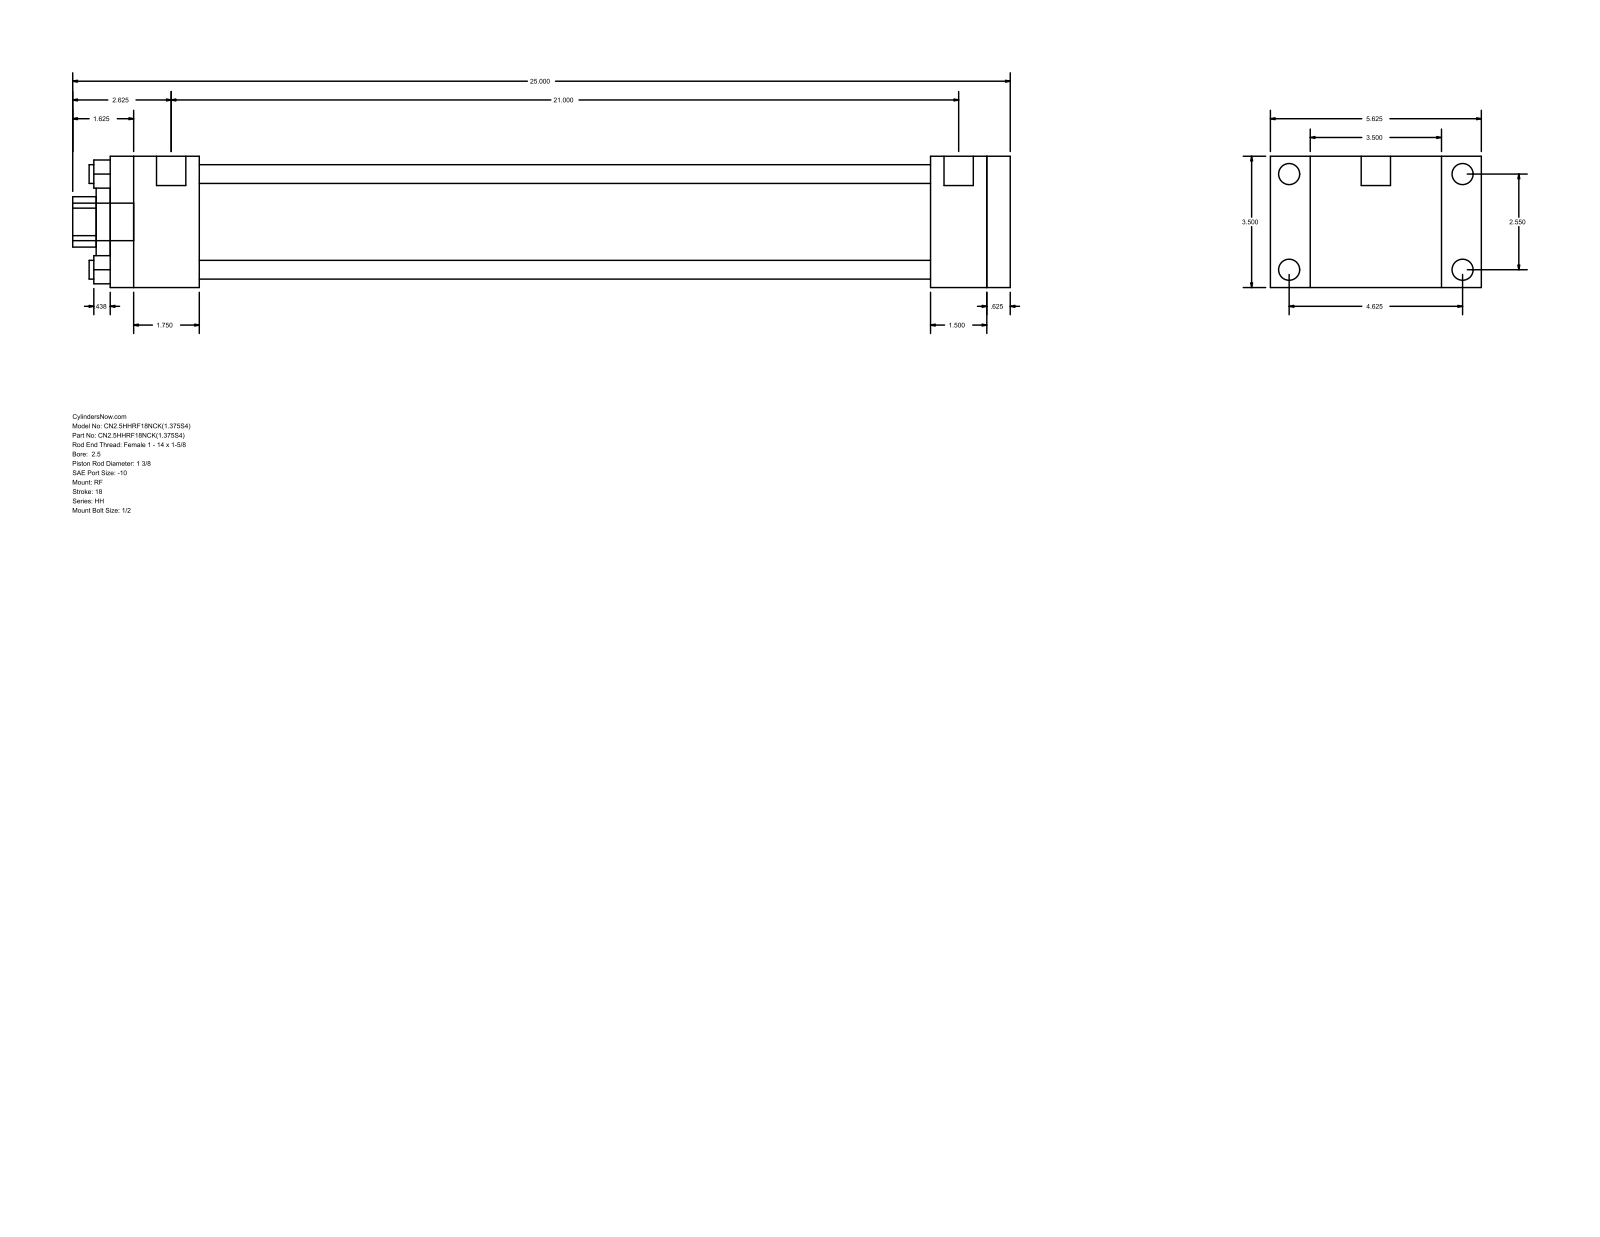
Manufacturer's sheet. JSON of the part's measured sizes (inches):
{"part_name": "HH_RF__0250_1.375", "step_written_by": "GSSL Pune (CONFIG_CONTROL_DESIGN)", "units": "inches", "bodies": {"solids": 0, "faces": 92, "planar": 64, "cylindrical": 28, "other": 0}, "overall_size": [25, 5.625, 3.5], "round_holes": [[0.5, 4], [1.375, 1], [2, 1], [2.875, 1]], "round_bosses_or_shafts": [[0.563, 4], [0.219, 4], [0.781, 2], [1, 1]], "partial_cylinders_radius": [[0.672, 1]], "face_to_face_distances": [3.5, 24, 0.625, 23.375, 2.375, 21, 21.625, 21.875, 19.5, 1.5], "hole_center_spacings": [1.803, 2.55, 3.606]}
